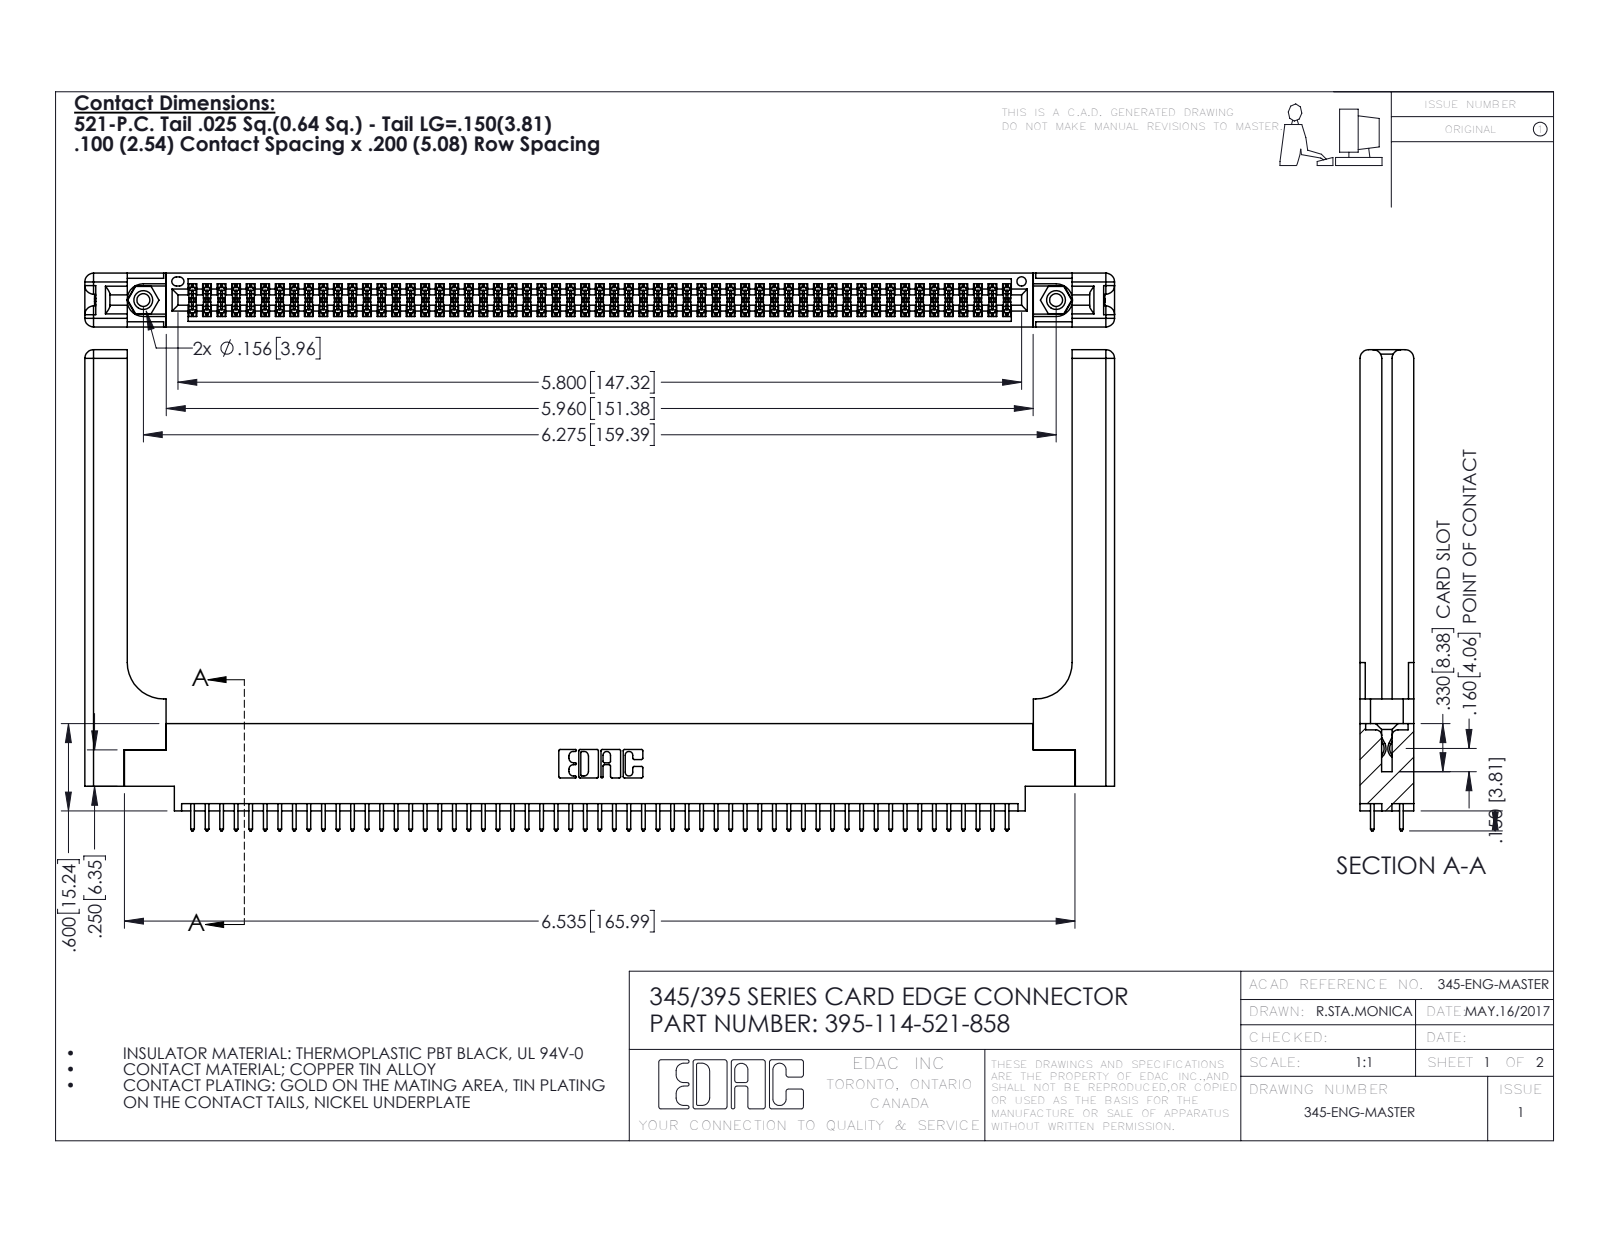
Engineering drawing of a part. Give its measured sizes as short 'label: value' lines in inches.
name: 345-292-001_345-293-121; 345-250-001_345-250-001-102; 395-114-521-858; 345-220-058_345-220-058 (+1 more)
written by: SolidWorks 2016 (CONFIG_CONTROL_DESIGN)
unit: in
bodies: 119 solids, 6086 faces (3994 planar, 2032 cylindrical, 60 other)
size: 7.079 × 3.307 × 0.37
volume: 1.582 in³; area: 48.02 in²
holes: 2× ⌀0.089, 2× ⌀0.125, 2× ⌀0.156, 1× ⌀0.064
bosses: 2× ⌀0.155
rounds: 171× R0.006, 114× R0.01, 22× R0.01, 16× R0.06, 6× R0.007, 6× R0.031, 3× R0.026, 2× R0.014
face distances: 0.072, 0.298, 0.37, 0.098, 0.272, 0.025, 0.2, 0.225, 0.175, 0.148
hole spacings: 0.27, 6.039, 6.275
